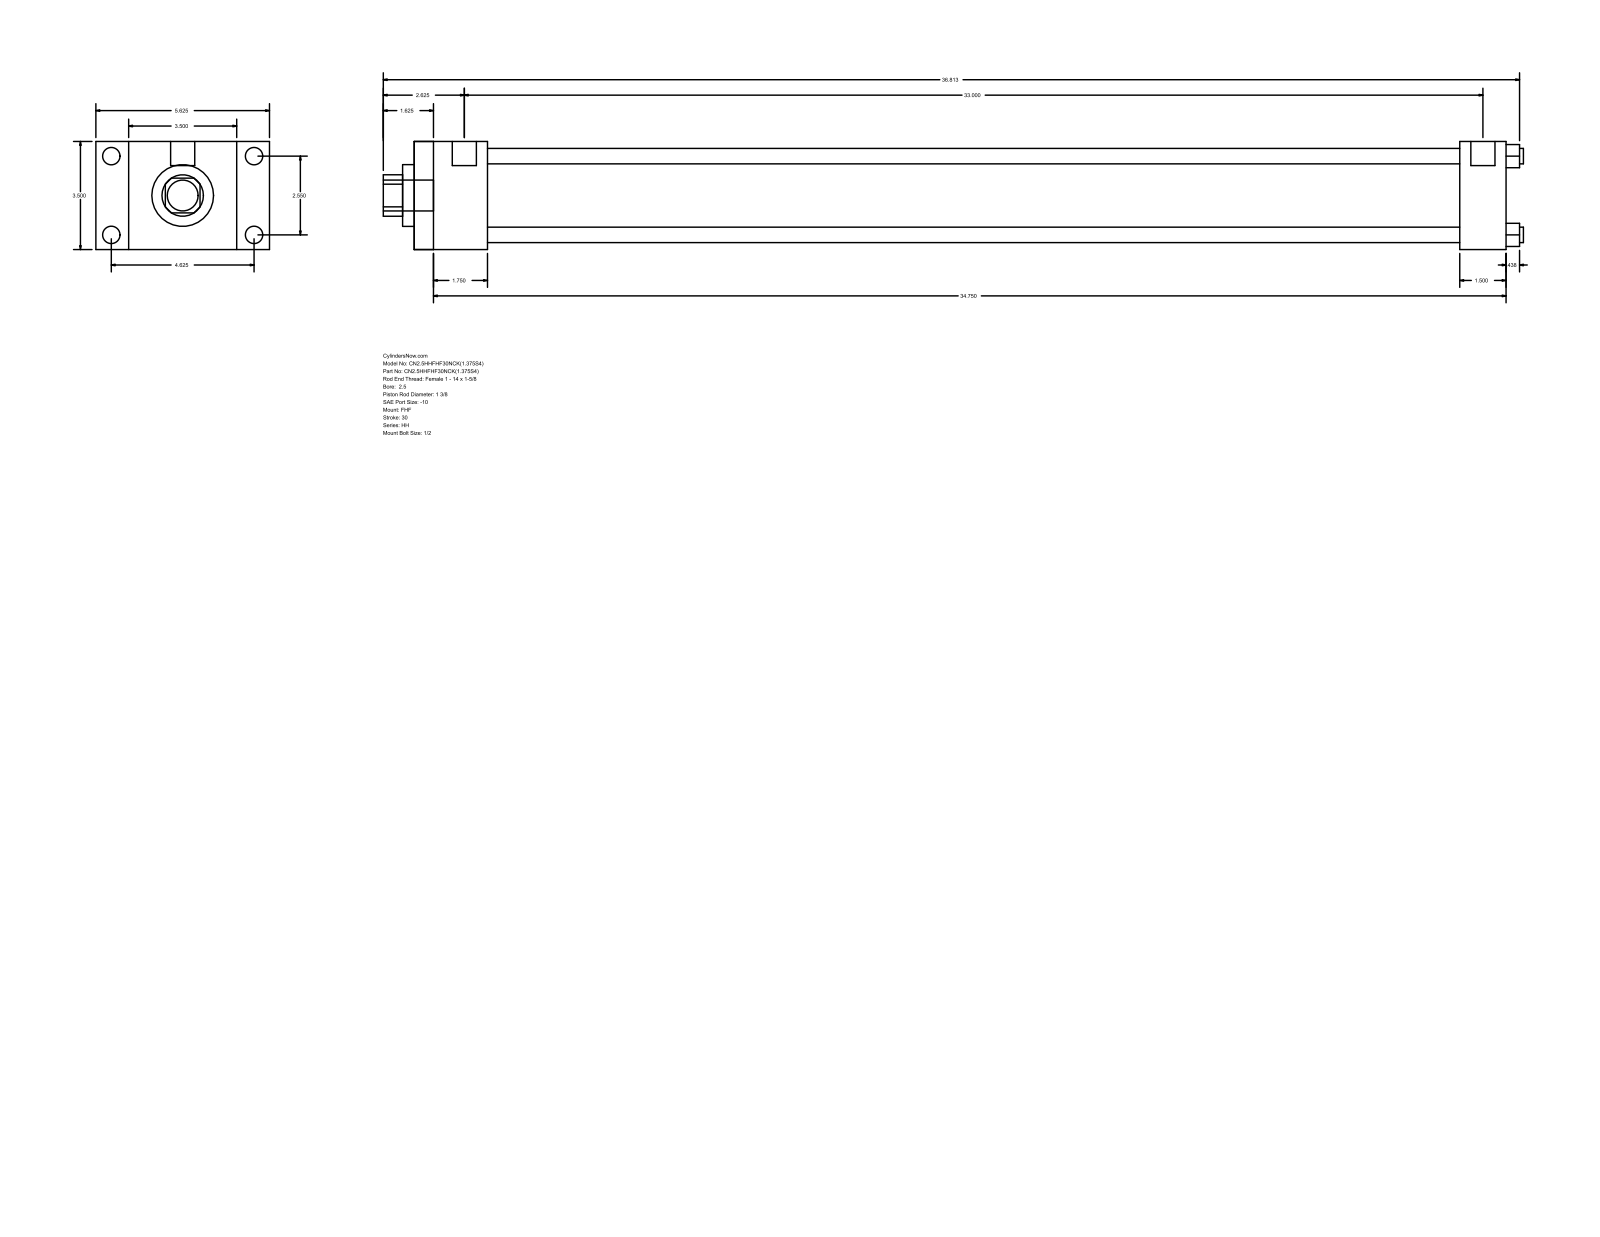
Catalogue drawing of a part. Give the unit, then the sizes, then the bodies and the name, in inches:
Units: inches
Overall size (bounding box): 36.937 × 5.625 × 3.5
Round holes (diameter × count): ⌀0.5 ×4, ⌀1.375 ×1, ⌀2 ×1, ⌀2.875 ×1
Round bosses / shafts (diameter × count): ⌀0.563 ×4, ⌀0.219 ×4, ⌀0.781 ×2, ⌀1 ×1
Partial cylindrical surfaces — rounded edges, fillets, slot ends (radius × count): R0.672 ×1
Main face-to-face distances: 3.5, 2.375, 1.063, 4.563, 35.375, 33, 5.625, 33.875, 31.5, 1.5
Hole centre spacings: 1.803, 2.55, 3.606
Bodies: 0 solids, 88 faces (60 planar, 28 cylindrical, 0 other)
Part name (STEP PRODUCT): HH_FHF__0250_1.375
STEP written by: GSSL Pune (CONFIG_CONTROL_DESIGN)
